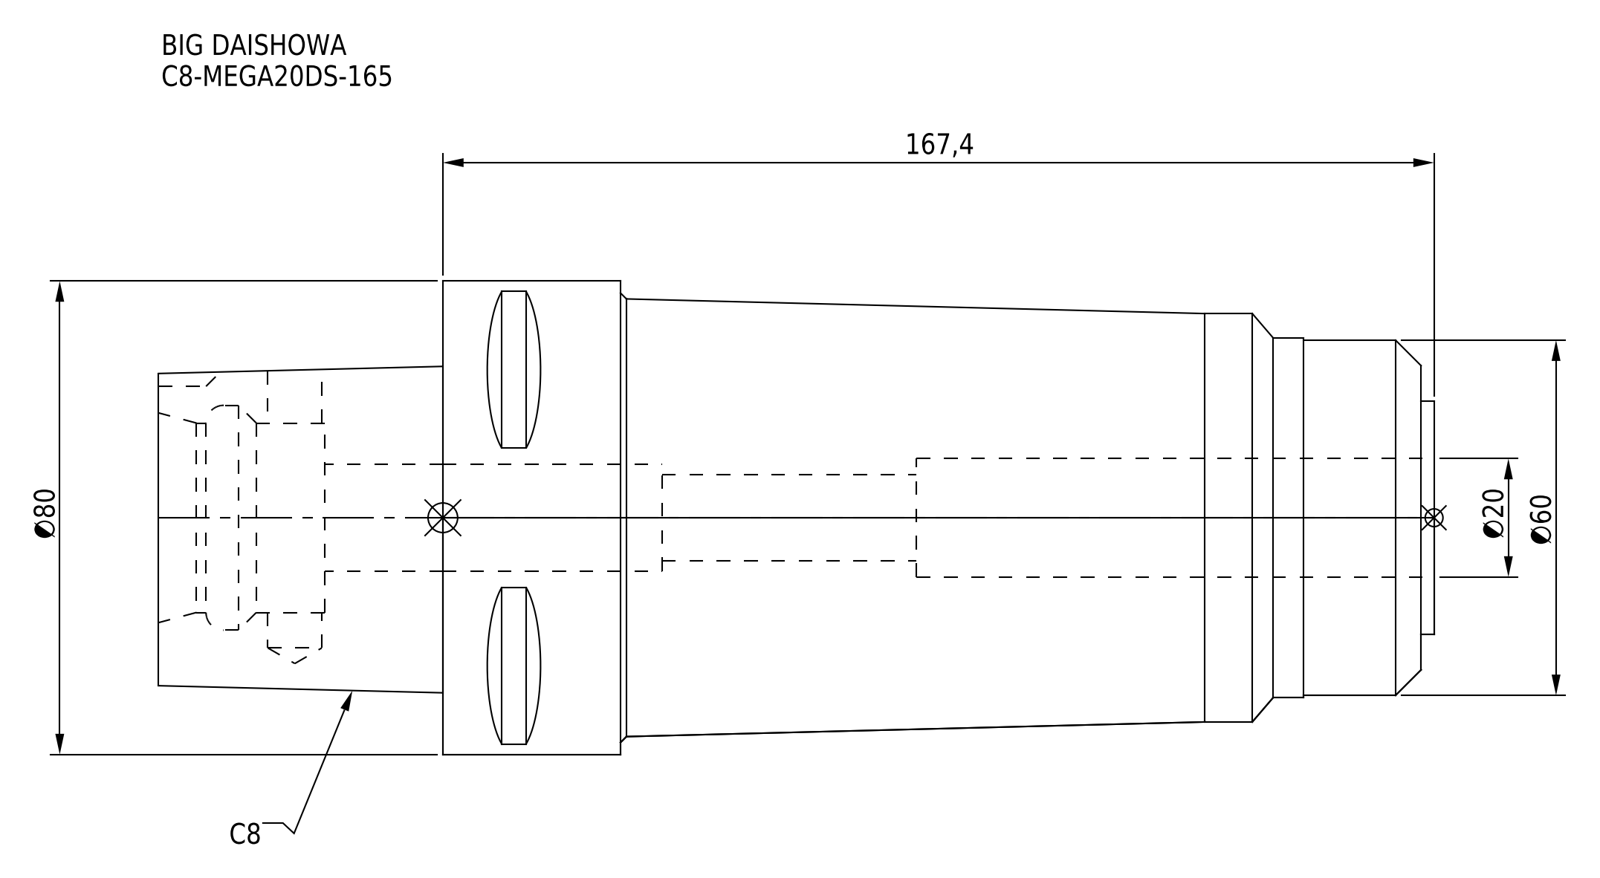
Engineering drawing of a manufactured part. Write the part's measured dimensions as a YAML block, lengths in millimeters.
part_name: "C8-MEGA20DS-165"
step_written_by: "CREO PARAMETRIC BY PTC INC, 2016380 (AUTOMOTIVE_DESIGN)"
units: millimeters
bodies: {solids: 1, faces: 76, planar: 31, cylindrical: 27, other: 18}
overall_size: [215.4, 80, 80]
volume: 691118
surface_area: 67832
round_holes:
  - {diameter: 9.1, count: 1}
  - {diameter: 14.5, count: 1}
  - {diameter: 18, count: 1}
  - {diameter: 20, count: 1}
  - {diameter: 32, count: 1}
  - {diameter: 38, count: 1}
round_bosses_or_shafts:
  - {diameter: 80, count: 1}
  - {diameter: 69, count: 1}
  - {diameter: 60.7, count: 1}
  - {diameter: 60, count: 1}
  - {diameter: 39.3, count: 1}
partial_cylinders:
  - {radius: 6, count: 1}
face_to_face_distances: [48, 167.4, 215.4, 2.2, 165.2, 213.2, 50, 20, 187.4, 185.2]
